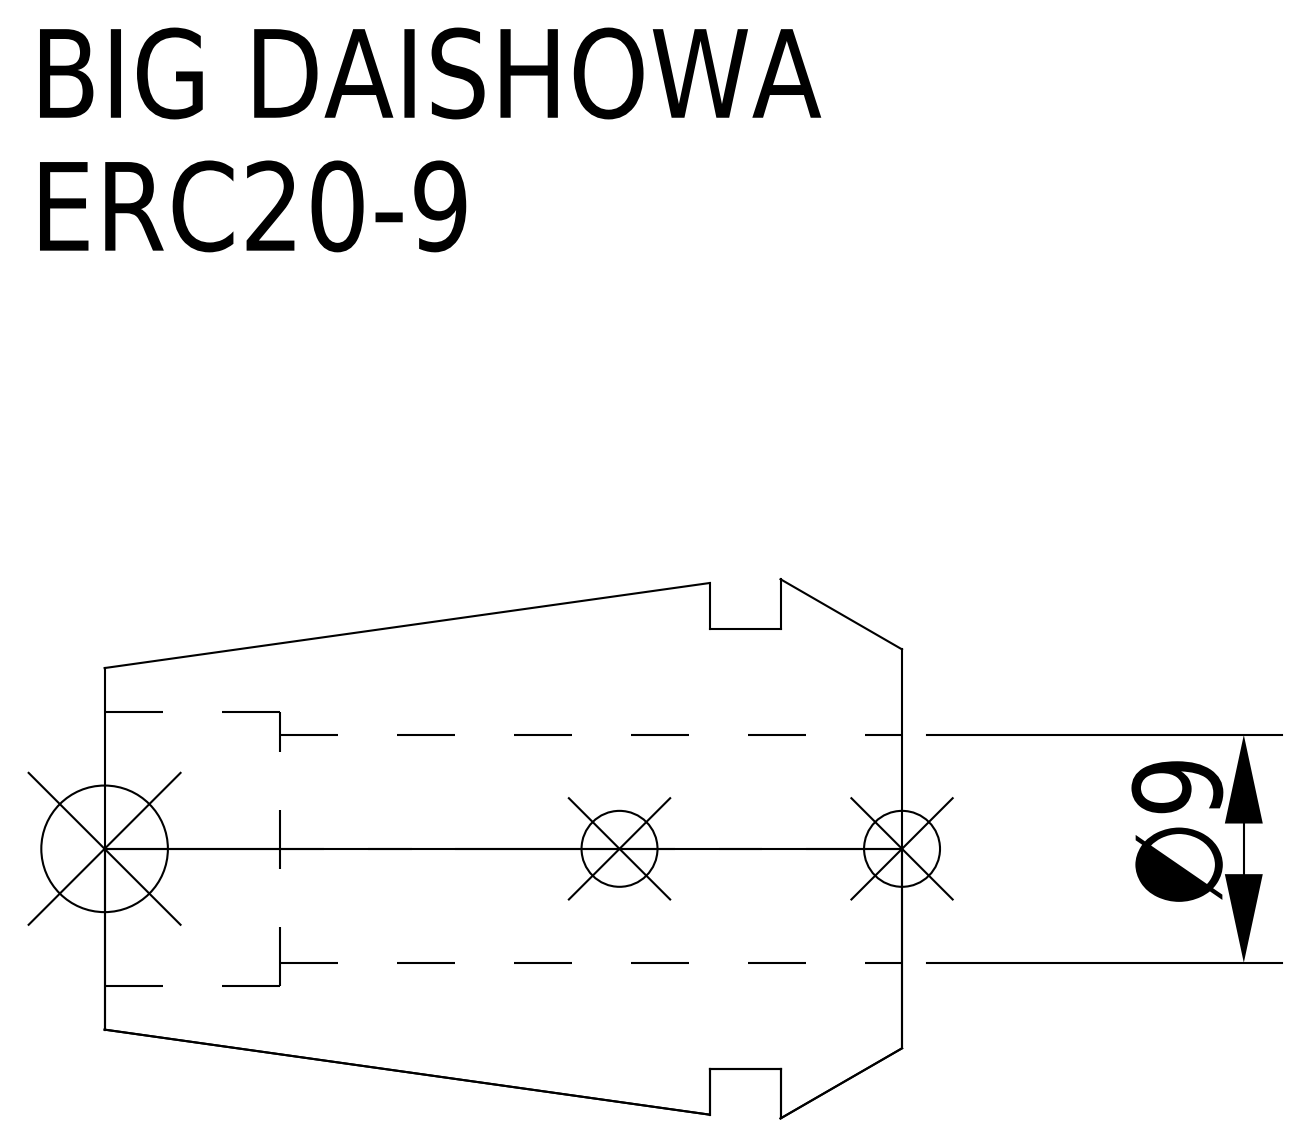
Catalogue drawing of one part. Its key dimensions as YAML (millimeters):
part_name: "ERC20-9"
step_written_by: "CREO PARAMETRIC BY PTC INC, 2016380 (AUTOMOTIVE_DESIGN)"
units: millimeters
bodies: {solids: 1, faces: 15, planar: 5, cylindrical: 6, other: 4}
overall_size: [31.5, 21.3, 21.3]
volume: 5685
surface_area: 3198
round_holes:
  - {diameter: 9, count: 1}
  - {diameter: 10.8, count: 1}
round_bosses_or_shafts:
  - {diameter: 17.4, count: 1}
face_to_face_distances: [4.8, 7.6, 2.8, 31.5, 26.7, 23.9, 24.58, 19.78, 16.98, 6.92]
